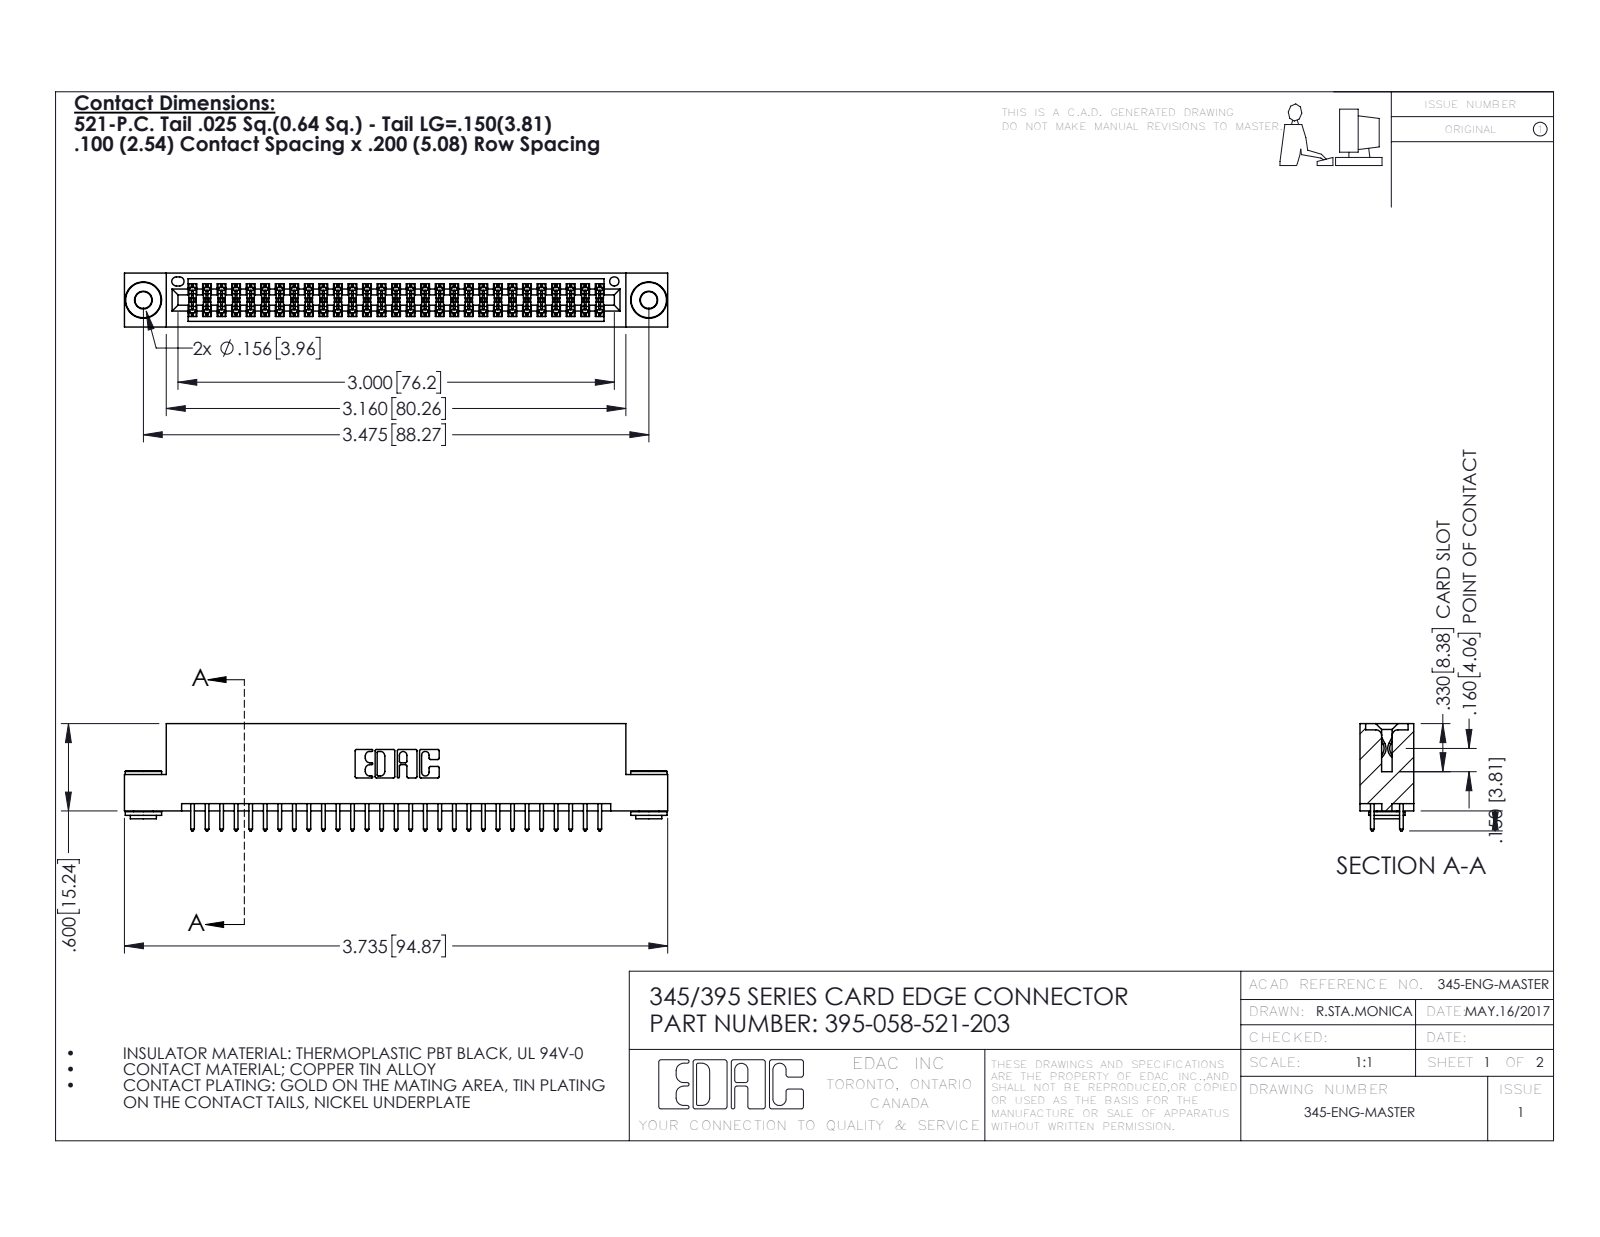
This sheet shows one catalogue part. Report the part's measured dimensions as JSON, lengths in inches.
{"part_name": "395-058-521-203; 345 Part_Flush Mounting Lugs - 0.156 Dia-TH; 345-292-001_345-293-121; 345-250-002_345-250-002-102", "step_written_by": "SolidWorks 2016 (CONFIG_CONTROL_DESIGN)", "units": "inches", "bodies": {"solids": 61, "faces": 3064, "planar": 2004, "cylindrical": 1052, "other": 8}, "overall_size": [3.735, 0.737, 0.37], "volume_in3": 0.555, "surface_area_in2": 20.52, "round_holes": [[0.116, 2], [0.156, 2], [0.064, 1]], "round_bosses_or_shafts": [[0.25, 2], [0.18, 2], [0.136, 2]], "partial_cylinders_radius": [[0.006, 87], [0.01, 58], [0.01, 22], [0.007, 6], [0.031, 6], [0.026, 3], [0.014, 2], [0.019, 2]], "face_to_face_distances": [0.072, 0.298, 0.2, 0.37, 0.025, 0.098, 0.272, 0.225, 0.175, 0.149], "hole_center_spacings": [0.27, 3.24, 3.475]}
